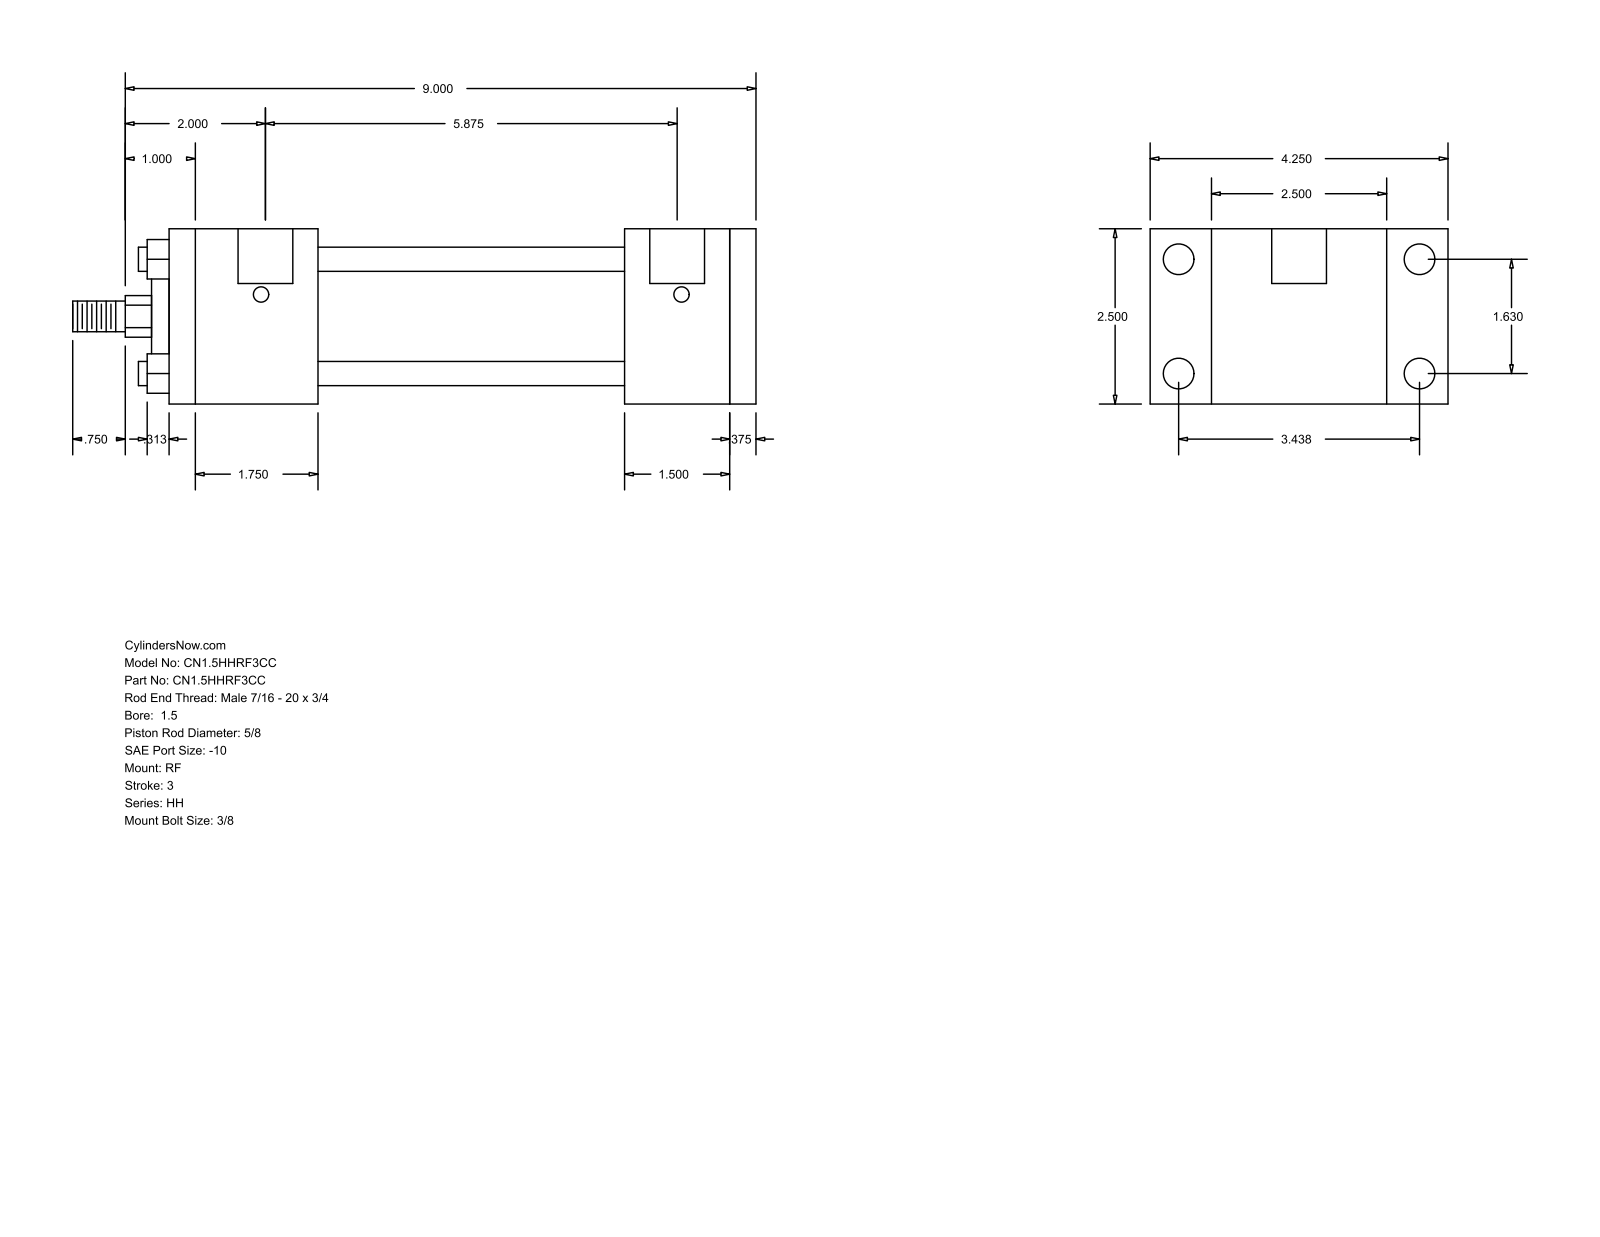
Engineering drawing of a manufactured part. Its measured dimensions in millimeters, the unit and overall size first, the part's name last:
Units: millimetres
Overall size (bounding box): 247.65 × 107.95 × 63.5
Round holes (diameter × count): ⌀5.56 ×4, ⌀11.13 ×4, ⌀19.84 ×2
Round bosses / shafts (diameter × count): ⌀8.76 ×4, ⌀44.45 ×1, ⌀28.57 ×1, ⌀15.88 ×1, ⌀11.11 ×1
Partial cylindrical surfaces — rounded edges, fillets, slot ends (radius × count): R7.54 ×1
Main face-to-face distances: 63.5, 212.72, 9.53, 38.1, 203.19, 47.63, 53.97, 165.09, 111.12, 149.22
Hole centre spacings: 41.4, 87.32, 96.64, 152.4, 1.58, 1.59, 149.23, 150.81
Bodies: 0 solids, 92 faces (64 planar, 28 cylindrical, 0 other)
Part name (STEP PRODUCT): HH_RF__0150_0.625
STEP written by: GSSL Pune (CONFIG_CONTROL_DESIGN)
